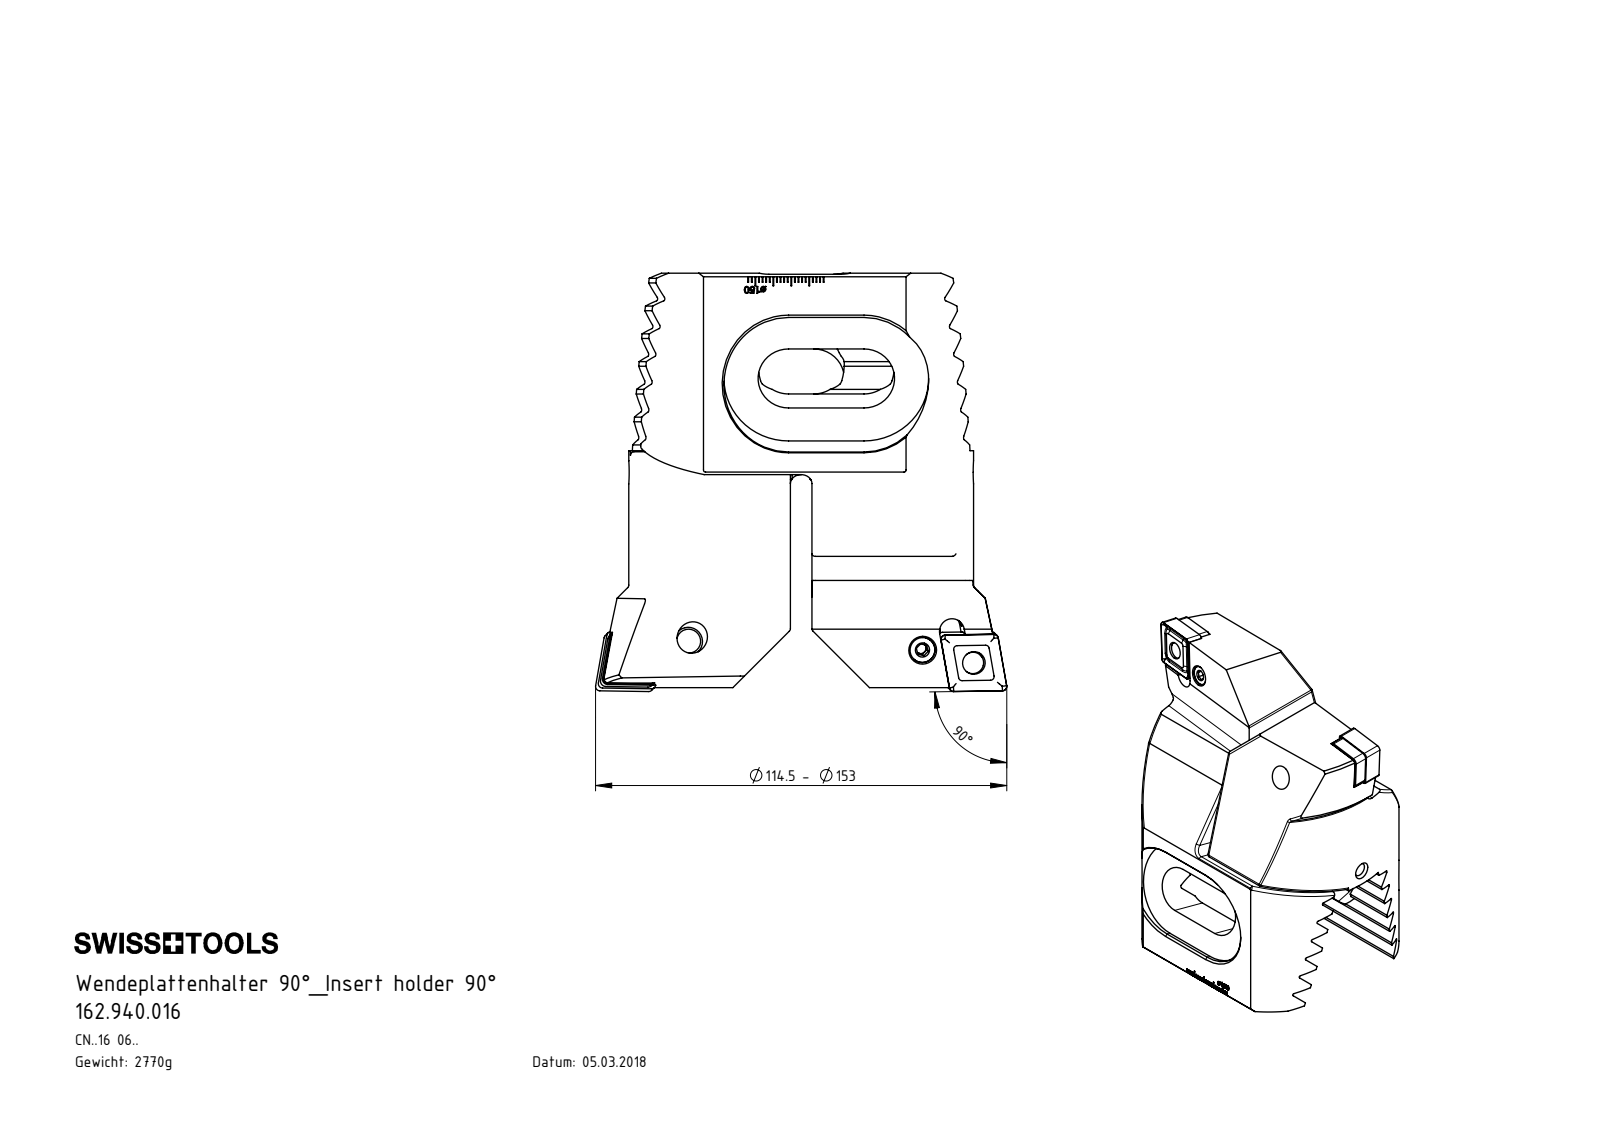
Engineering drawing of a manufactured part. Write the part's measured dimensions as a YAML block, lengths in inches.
part_name: "Z94-xxx.001.067_C_CN16; WCE-ER3.101.000_A; 162.940.016; Z72-ER3.001.030 (+5 more)"
step_written_by: "SolidWorks 2017 (CONFIG_CONTROL_DESIGN)"
units: inches
bodies: {solids: 14, faces: 960, planar: 534, cylindrical: 168, other: 258}
overall_size: [4.583, 4.508, 2.961]
volume: 21.48
surface_area: 109.1
round_holes:
  - {diameter: 0.079, count: 2}
  - {diameter: 0.25, count: 2}
  - {diameter: 0.276, count: 2}
  - {diameter: 0.317, count: 2}
  - {diameter: 0.331, count: 2}
  - {diameter: 0.197, count: 1}
round_bosses_or_shafts:
  - {diameter: 0.236, count: 3}
  - {diameter: 0.315, count: 2}
  - {diameter: 0.311, count: 2}
  - {diameter: 0.252, count: 2}
  - {diameter: 0.14, count: 2}
  - {diameter: 0.157, count: 1}
partial_cylinders:
  - {radius: 0.039, count: 16}
  - {radius: 0.023, count: 12}
  - {radius: 0.047, count: 8}
  - {radius: 0.059, count: 8}
  - {radius: 0.118, count: 6}
  - {radius: 0.138, count: 6}
  - {radius: 0.012, count: 4}
  - {radius: 0.335, count: 4}
face_to_face_distances: [0.273, 0.546, 0.819, 1.091, 0.519, 0.236, 0.818, 0.063, 0.545, 1.091]
hole_center_spacings: [0.581, 0.591, 0.984, 1.902]
